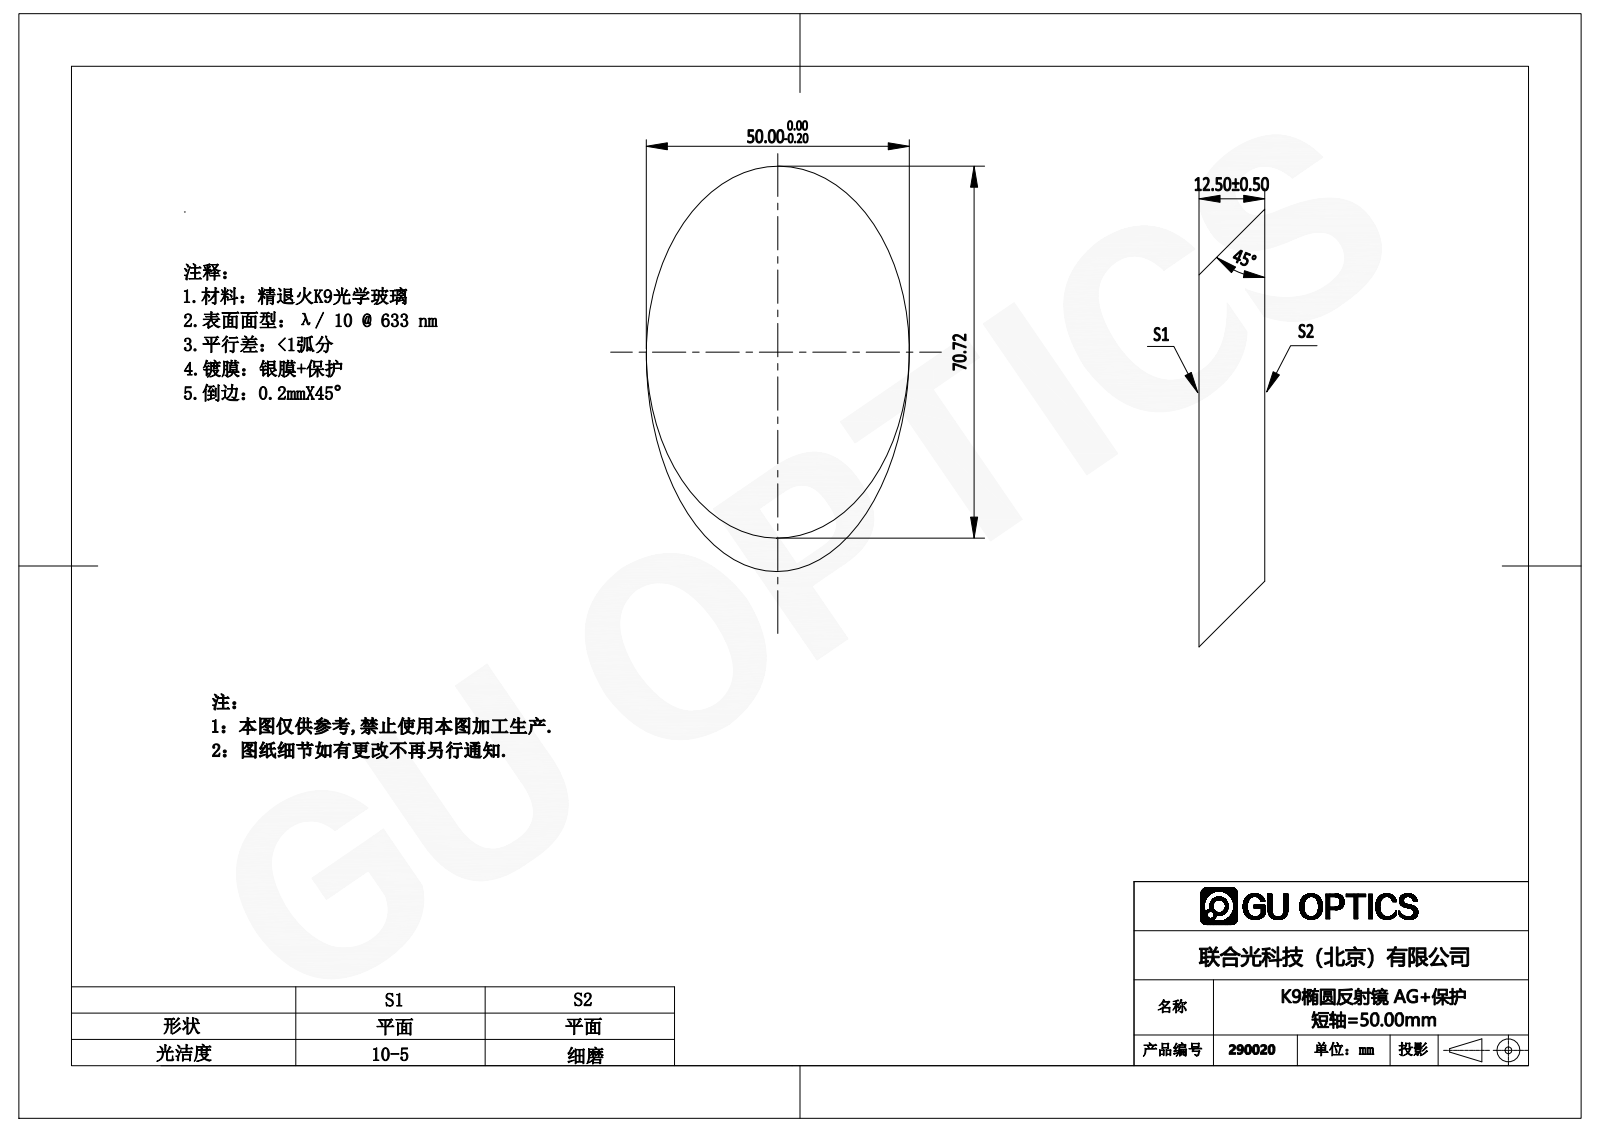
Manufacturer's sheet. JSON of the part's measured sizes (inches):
{"part_name": "290004", "step_written_by": "SolidWorks 2016 (AUTOMOTIVE_DESIGN)", "units": "inches", "bodies": {"solids": 1, "faces": 4, "planar": 2, "cylindrical": 0, "other": 2}, "overall_size": [3.276, 1.969, 0.492], "volume_in3": 2.119, "surface_area_in2": 12.91, "face_to_face_distances": [0.492]}
